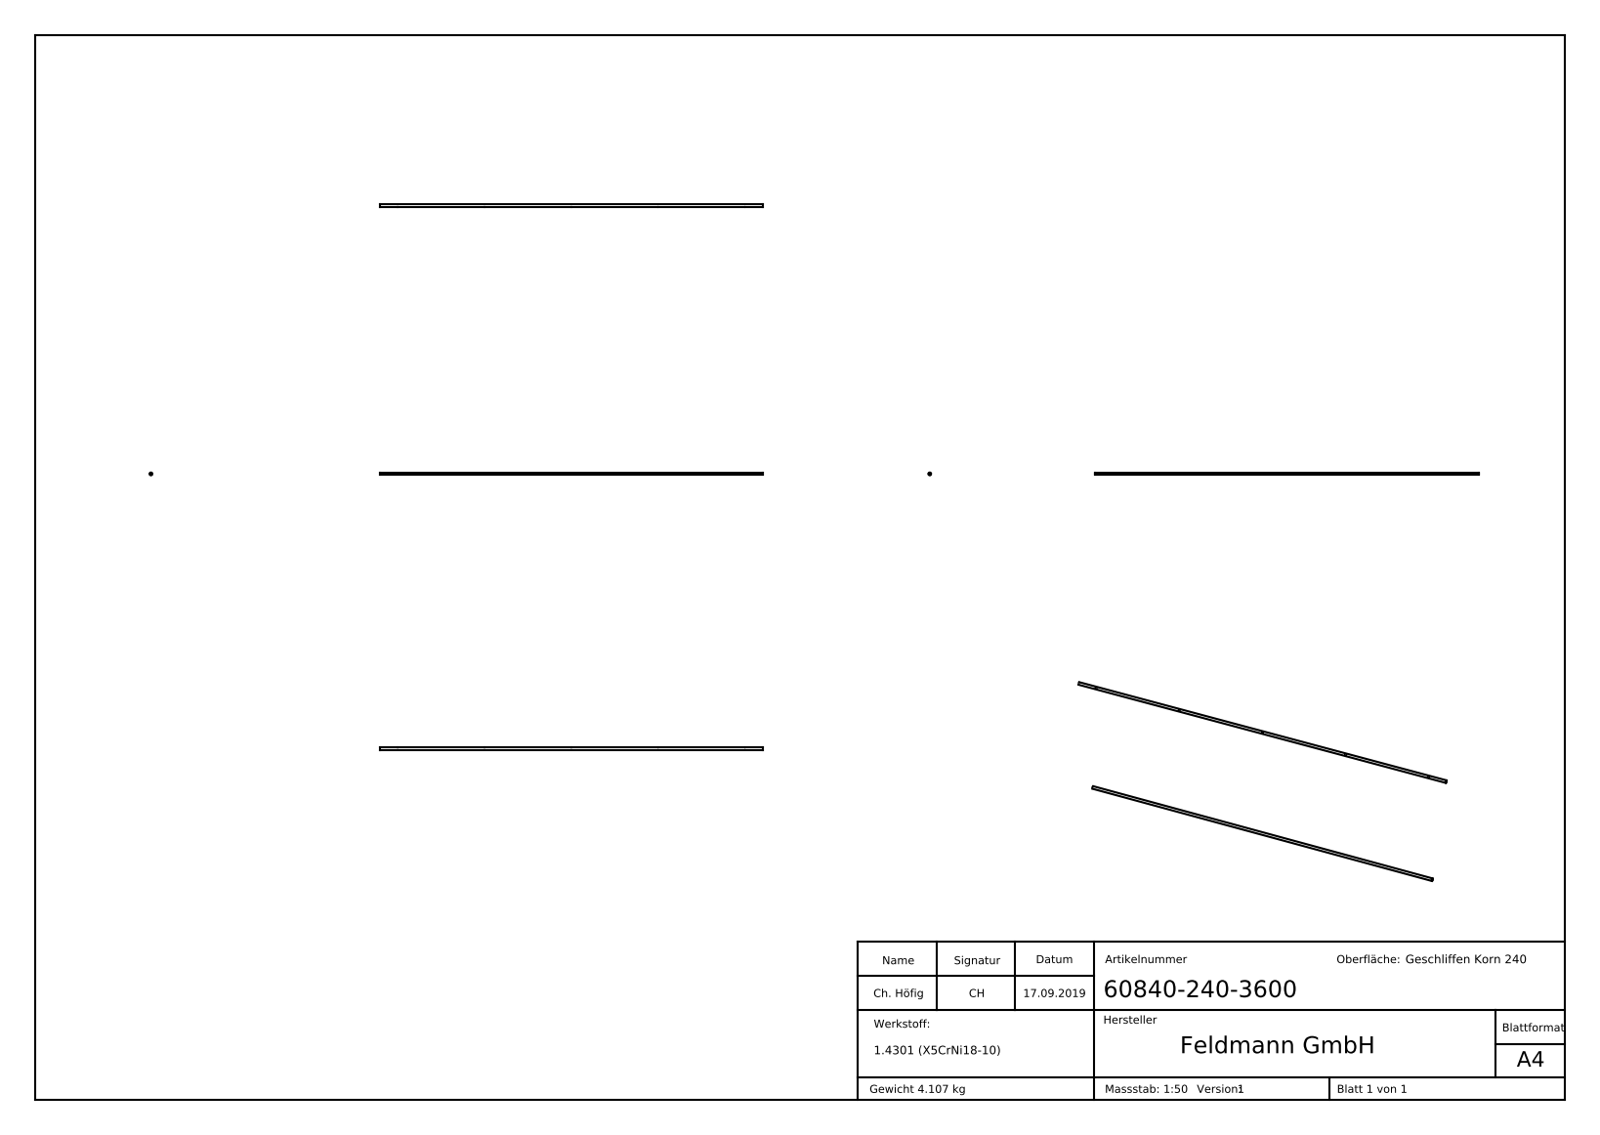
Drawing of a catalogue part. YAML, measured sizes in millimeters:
part_name: "60840-240-3600"
step_written_by: "SolidWorks 2015 (CONFIG_CONTROL_DESIGN)"
units: millimeters
bodies: {solids: 1, faces: 312, planar: 105, cylindrical: 59, other: 148}
overall_size: [3600, 25, 25]
volume: 519880
surface_area: 520401
round_holes:
  - {diameter: 6.8, count: 5}
  - {diameter: 21, count: 1}
round_bosses_or_shafts:
  - {diameter: 25, count: 1}
partial_cylinders:
  - {radius: 10.6, count: 1}
face_to_face_distances: [3600, 2.97, 0.39, 3.66, 3.27, 3.67, 3.09, 3.36, 3.02, 2.9]
hole_center_spacings: [815, 1630, 2445, 3260]
